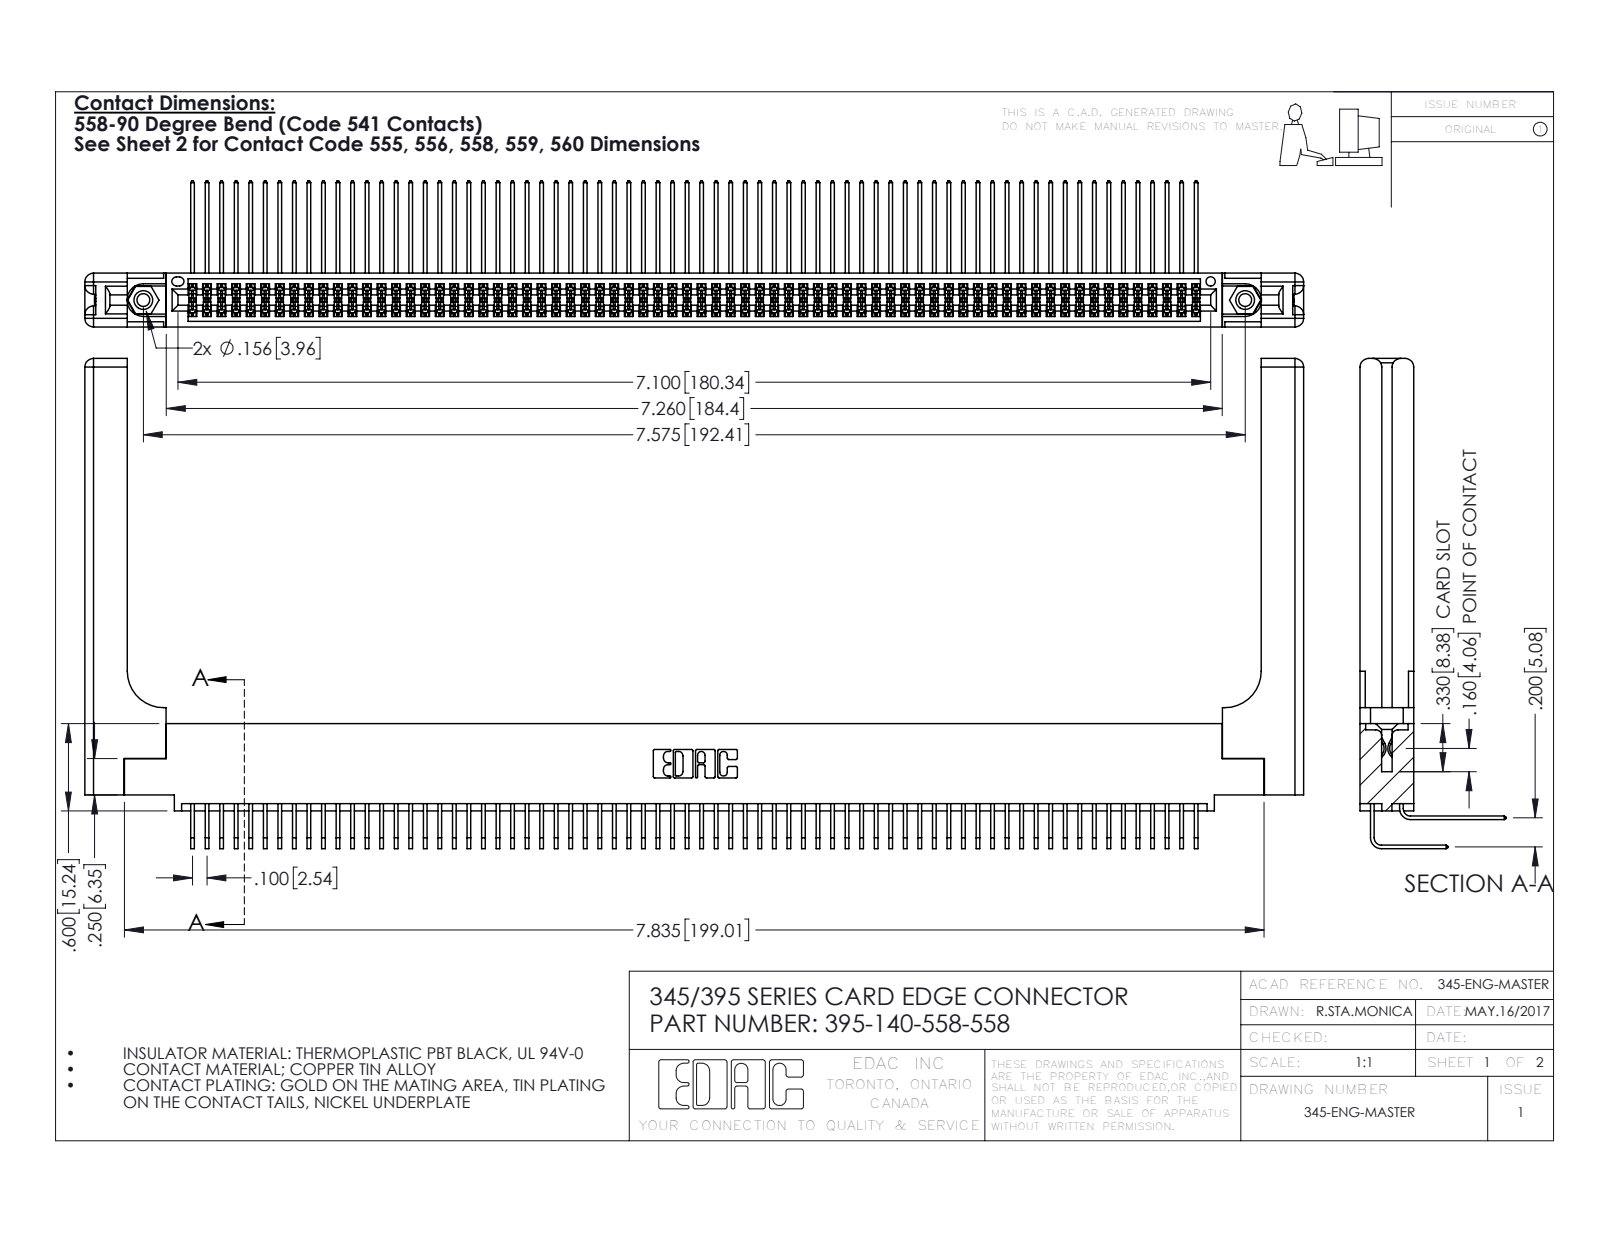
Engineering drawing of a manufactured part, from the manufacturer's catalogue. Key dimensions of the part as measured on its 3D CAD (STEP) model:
Part name (STEP PRODUCT): 345 Part_0.110 Offset - 0.156 Dia-TH; 345-292-001_558 Tail - 2; 345-220-058_345-220-058; 395-140-558-558 (+2 more)
STEP written by: SolidWorks 2016 (CONFIG_CONTROL_DESIGN)
Units: inches
Bodies: 145 solids, 7666 faces (5132 planar, 2474 cylindrical, 60 other)
Overall size (bounding box): 8.379 × 3.369 × 1.005
Volume: 1.839 in³ · Surface area: 64.36 in²
Round holes (diameter × count): ⌀0.089 ×2, ⌀0.125 ×2, ⌀0.156 ×2, ⌀0.064 ×1
Round bosses / shafts (diameter × count): ⌀0.155 ×2
Partial cylindrical surfaces — rounded edges, fillets, slot ends (radius × count): R0.006 ×279, R0.01 ×22, R0.06 ×16, R0.007 ×6, R0.031 ×6, R0.026 ×3, R0.014 ×2, R0.019 ×2
Main face-to-face distances: 0.072, 0.298, 0.37, 0.2, 0.098, 0.272, 0.025, 0.225, 0.025, 0.175
Hole centre spacings: 0.27, 7.339, 7.575
